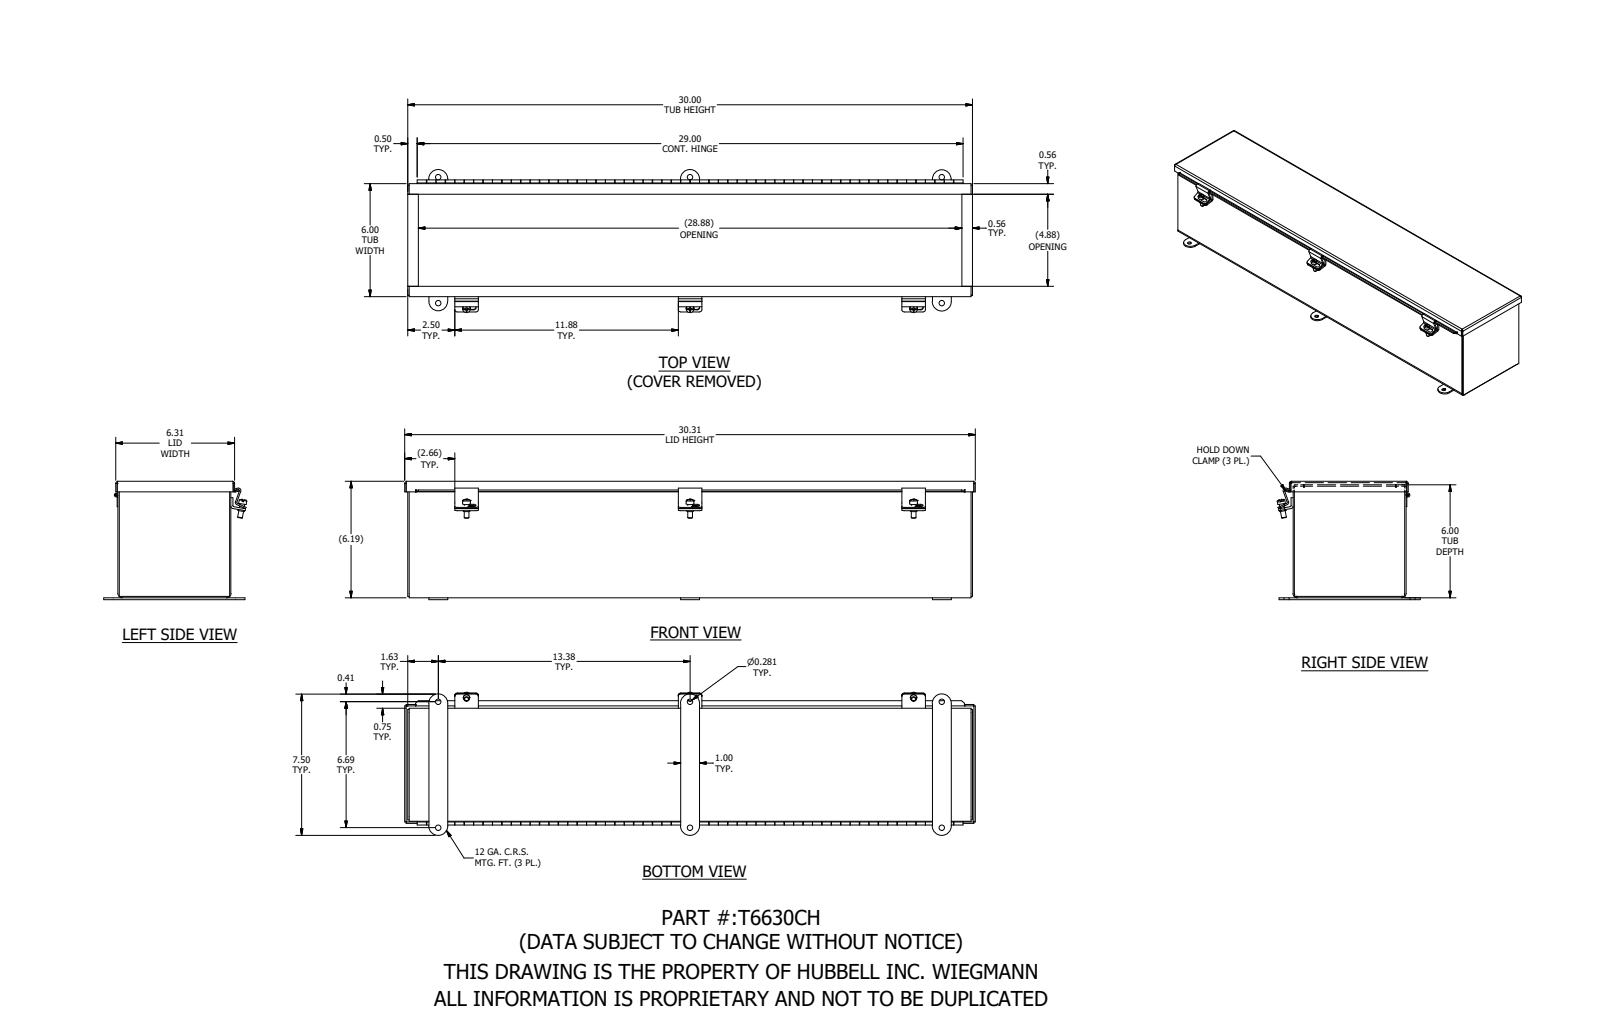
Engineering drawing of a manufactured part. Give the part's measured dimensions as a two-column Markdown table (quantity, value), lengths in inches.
| quantity | value |
| --- | --- |
| part name | T6630CH |
| STEP written by | SolidWorks 2021 (AUTOMOTIVE_DESIGN) |
| units | inches |
| bodies | 19 solids, 741 faces (378 planar, 340 cylindrical, 23 other) |
| overall size | 30.313 × 7.595 × 6.283 |
| volume | 68.67 in³ |
| surface area | 1 910 in² |
| round holes (diameter × count) | 0.281 × 6, 0.196 × 3, 0.116 × 1 |
| round bosses / shafts (diameter × count) | 0.41 × 3, 0.344 × 3, 0.25 × 3, 0.2 × 1, 0.1 × 1 |
| partial cylindrical surfaces (radius × count) | 0.125 × 12, 0.031 × 9, 0.105 × 9, 0.133 × 6, 0.5 × 6, 0.063 × 3, 0.126 × 3, 0.156 × 2 |
| main face-to-face distances | 0.074, 5.926, 6.115, 6, 5.852, 6.189, 6.041, 29.926, 0.189, 0.116 |
| hole center spacings | 6.687, 13.375, 13.375, 14.954, 14.954, 26.75, 27.573, 11.875 |
